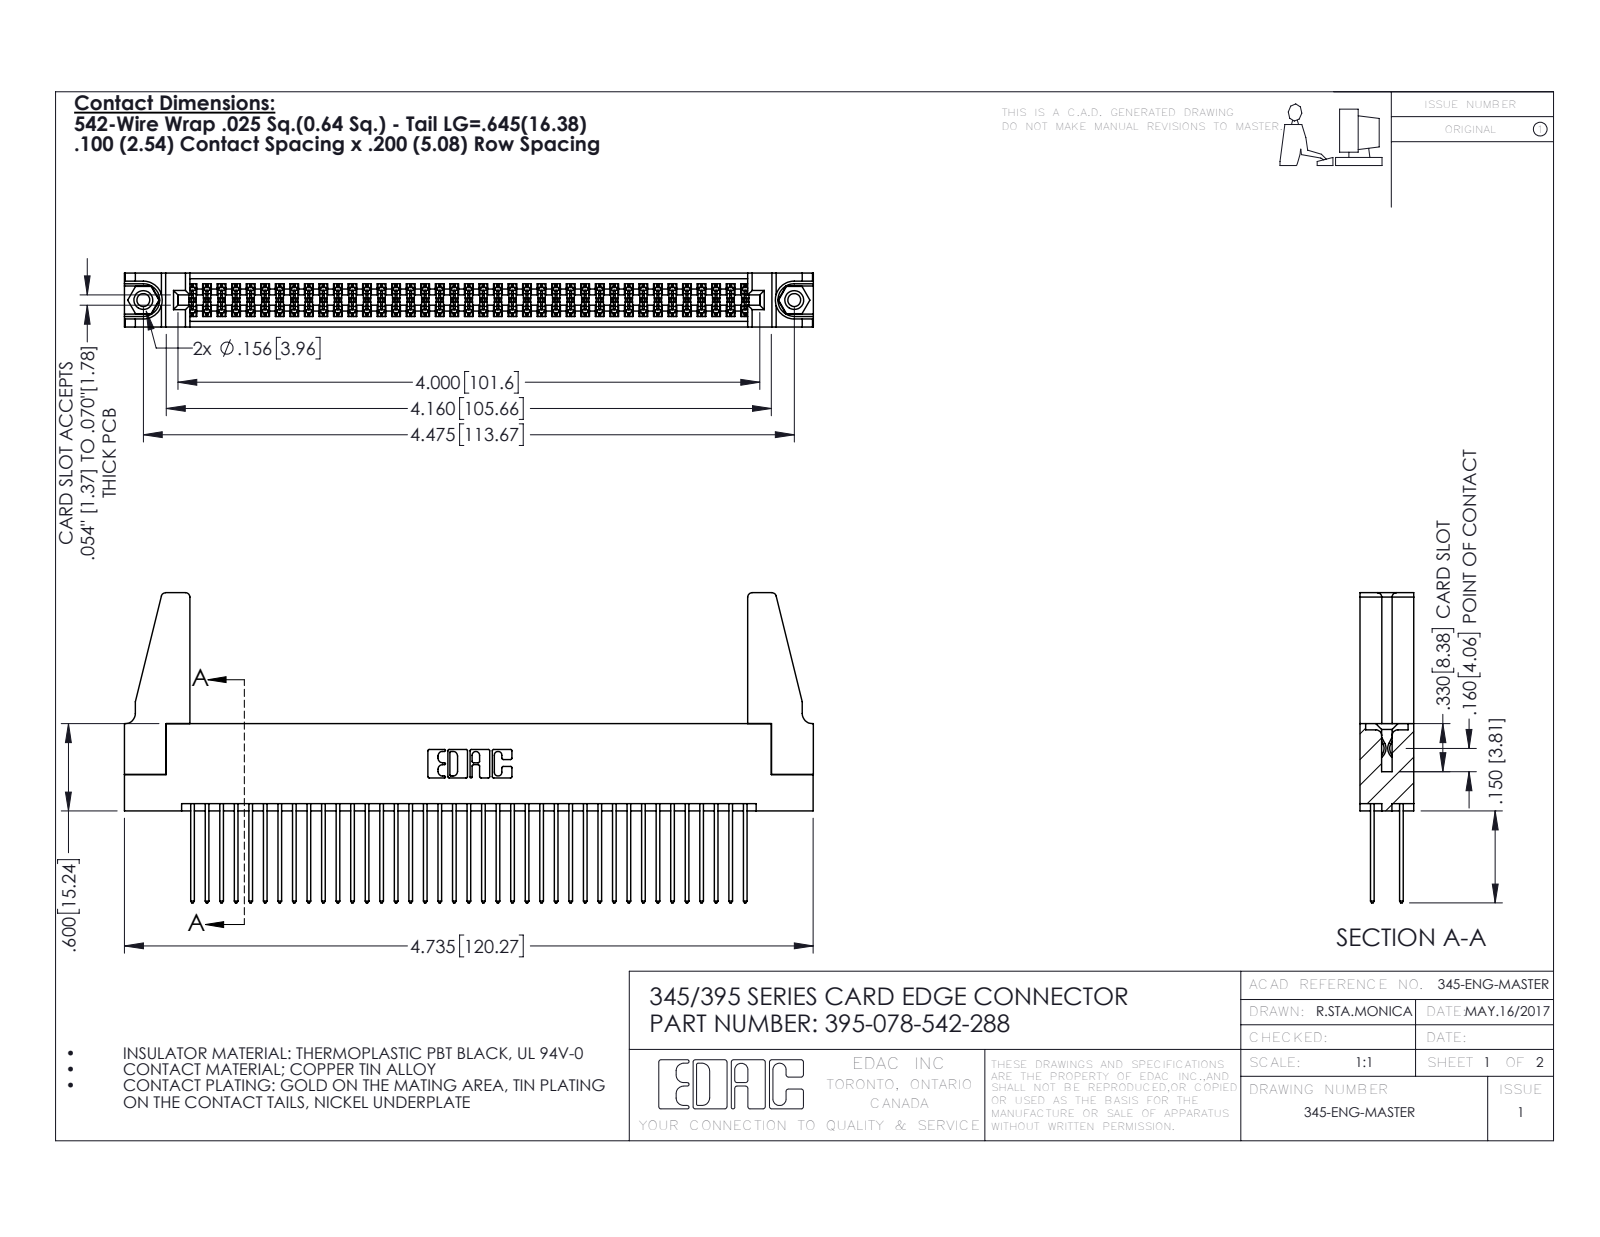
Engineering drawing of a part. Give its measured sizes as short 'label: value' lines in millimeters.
name: 345 Part_Flush Mounting Lugs - 0.156 Dia-TH; 345-292-001_345-293-142; 345-250-001_345-250-001-102; 345-220-078_345-220-088 (+1 more)
written by: SolidWorks 2016 (CONFIG_CONTROL_DESIGN)
unit: mm
bodies: 83 solids, 4150 faces (2726 planar, 1408 cylindrical, 16 other)
size: 120.3 × 54.2 × 9.4
volume: 15 300 mm³; area: 22 540 mm²
holes: 2× ⌀2.3, 2× ⌀3.2, 2× ⌀4, 1× ⌀1.6
bosses: 2× ⌀3.9
rounds: 117× R0.2, 78× R0.3, 22× R0.3, 8× R0.8, 6× R0.2, 6× R0.8, 3× R0.7, 2× R0.4
face distances: 1.8, 7.6, 5.1, 2.5, 6.9, 0.6, 9.4, 5.7, 4.4, 3.8
hole spacings: 6.9, 107.7, 113.7
